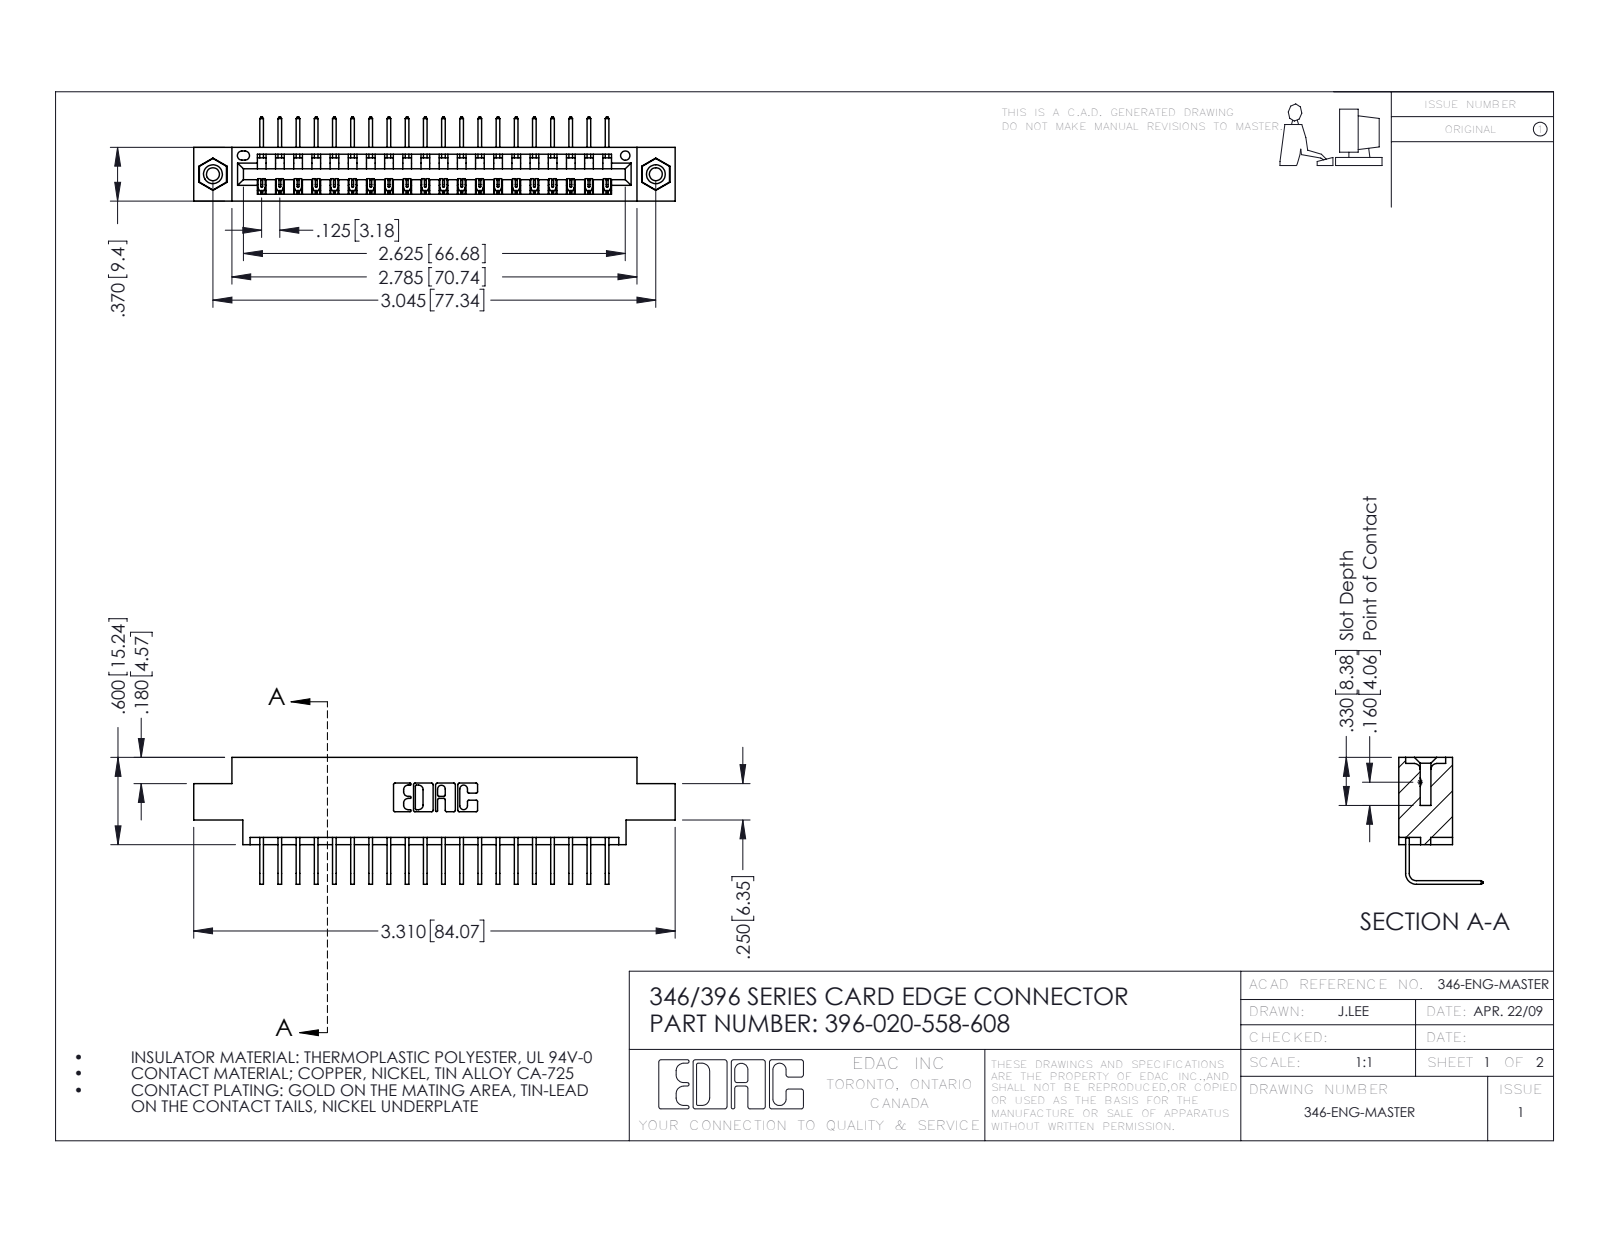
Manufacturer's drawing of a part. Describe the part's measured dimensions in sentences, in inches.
The part is named "346 Part_0.170 Offset - 0.156 Dia-TI; 396-020-558-608; 345-292-001_558 Tail - 2; 345-250-001_345-250-003-102". Its 3-D file was written by "SolidWorks 2016 (CONFIG_CONTROL_DESIGN)". It is 23 solids with 1386 faces: 952 planar, 418 cylindrical and 16 other. Overall it measures 3.31 by 0.873 by 0.58 inches. Its volume is 0.476 cubic inches and its surface area 15.64 square inches. Round holes: 2 of diameter 0.089, 2 of diameter 0.125, 2 of diameter 0.156, 1 of diameter 0.064. Round bosses or shafts: 2 of diameter 0.155. Partial cylindrical surfaces (rounded edges, fillets, slot ends): 40 of radius 0.006, 22 of radius 0.01, 6 of radius 0.007, 6 of radius 0.031, 3 of radius 0.026, 2 of radius 0.031, 2 of radius 0.04, 1 of radius 0.014. The main face-to-face distances are 0.322, 0.048, 0.37, 0.25, 0.298, 0.025, 0.072, 0.222, 0.148, 0.1. The hole center spacings are 0.246, 2.837, 3.045.
